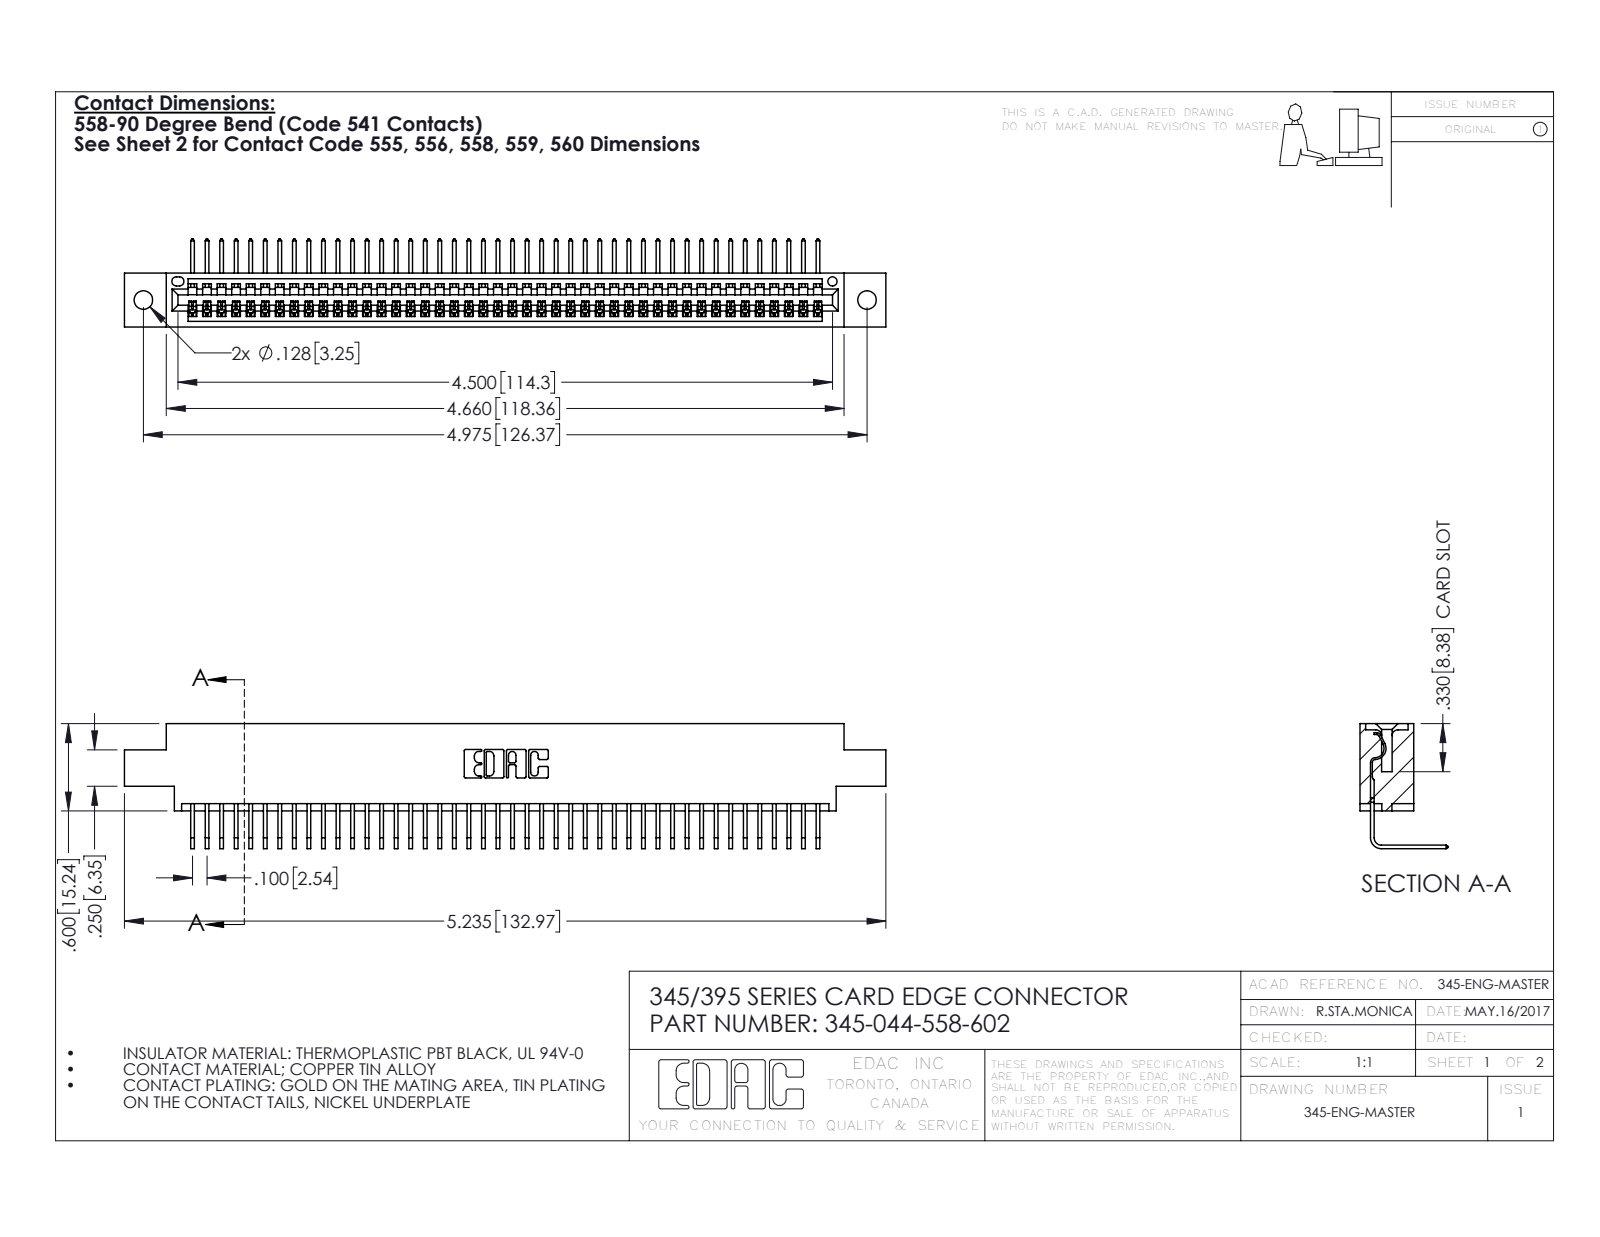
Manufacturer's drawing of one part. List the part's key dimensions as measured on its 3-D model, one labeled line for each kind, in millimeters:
Part name (STEP PRODUCT): 345-044-558-602; 345-292-001_558 Tail - 2; 345 Part_0.170 Offset - 0.128 Dia
STEP written by: SolidWorks 2016 (CONFIG_CONTROL_DESIGN)
Units: millimetres
Bodies: 45 solids, 2770 faces (1932 planar, 838 cylindrical, 0 other)
Overall size (bounding box): 133 × 21.8 × 15.4
Volume: 12 600 mm³ · Surface area: 17 540 mm²
Round holes (diameter × count): ⌀3.3 ×2, ⌀1.6 ×1
Partial cylindrical surfaces — rounded edges, fillets, slot ends (radius × count): R0.2 ×88, R0.3 ×22, R0.2 ×6, R0.8 ×6, R0.7 ×3, R0.8 ×2, R1 ×2, R0.4 ×1
Main face-to-face distances: 1.8, 7.6, 9.4, 5.1, 2.5, 6.9, 0.6, 5.7, 4.4, 3.8
Hole centre spacings: 6.9, 120.4, 126.4
